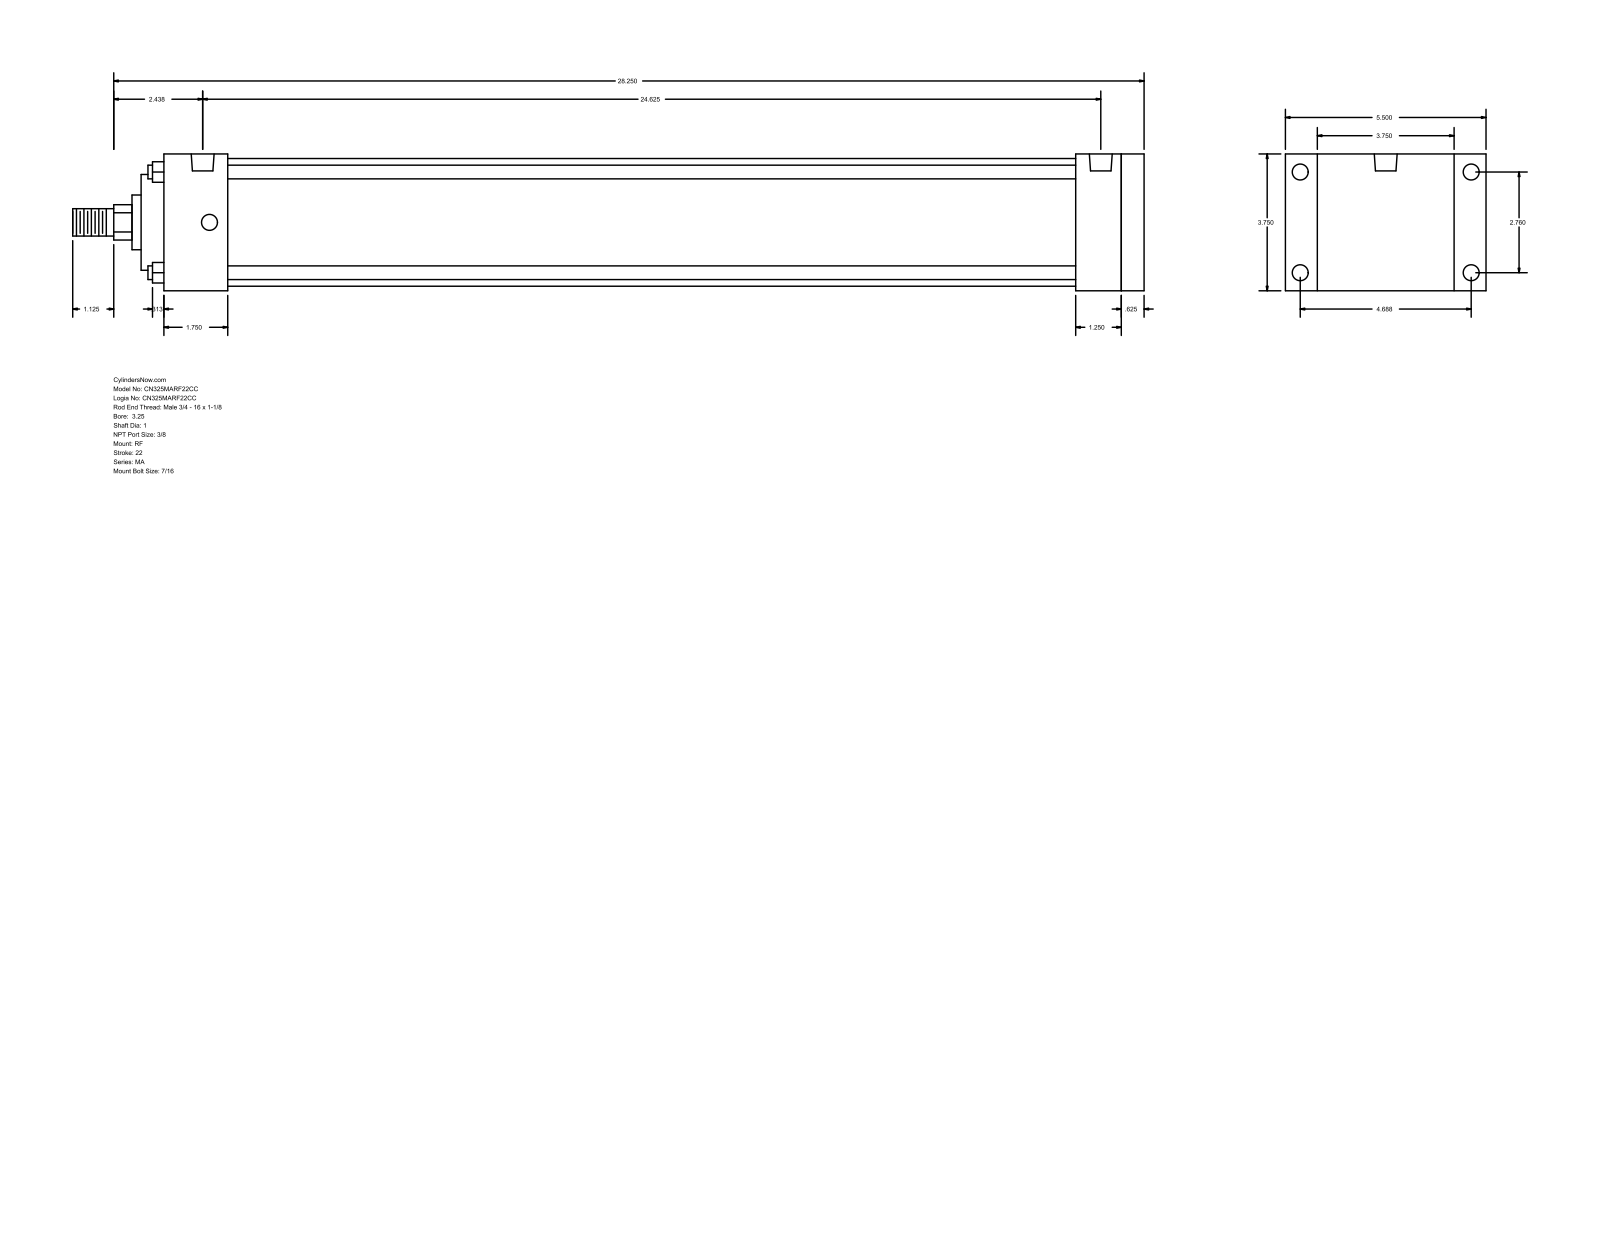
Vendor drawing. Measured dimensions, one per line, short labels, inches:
name: MA_RF__0325_1
written by: GSSL Pune (CONFIG_CONTROL_DESIGN)
unit: in
bodies: 0 solids, 94 faces (65 planar, 29 cylindrical, 0 other)
size: 29.375 × 5.5 × 3.75
holes: 8× ⌀0.437, 2× ⌀0.627
bosses: 4× ⌀0.375, 1× ⌀3.5, 1× ⌀2.625, 1× ⌀1.5, 1× ⌀1, 1× ⌀0.75
rounds: 1× R0.484
face distances: 3.75, 26.875, 26.25, 0.625, 0.875, 4.625, 25, 1.25, 1.875, 1.75
hole spacings: 2.76, 4.687, 5.439, 24.25, 0.187, 0.188, 24.437, 24.438
